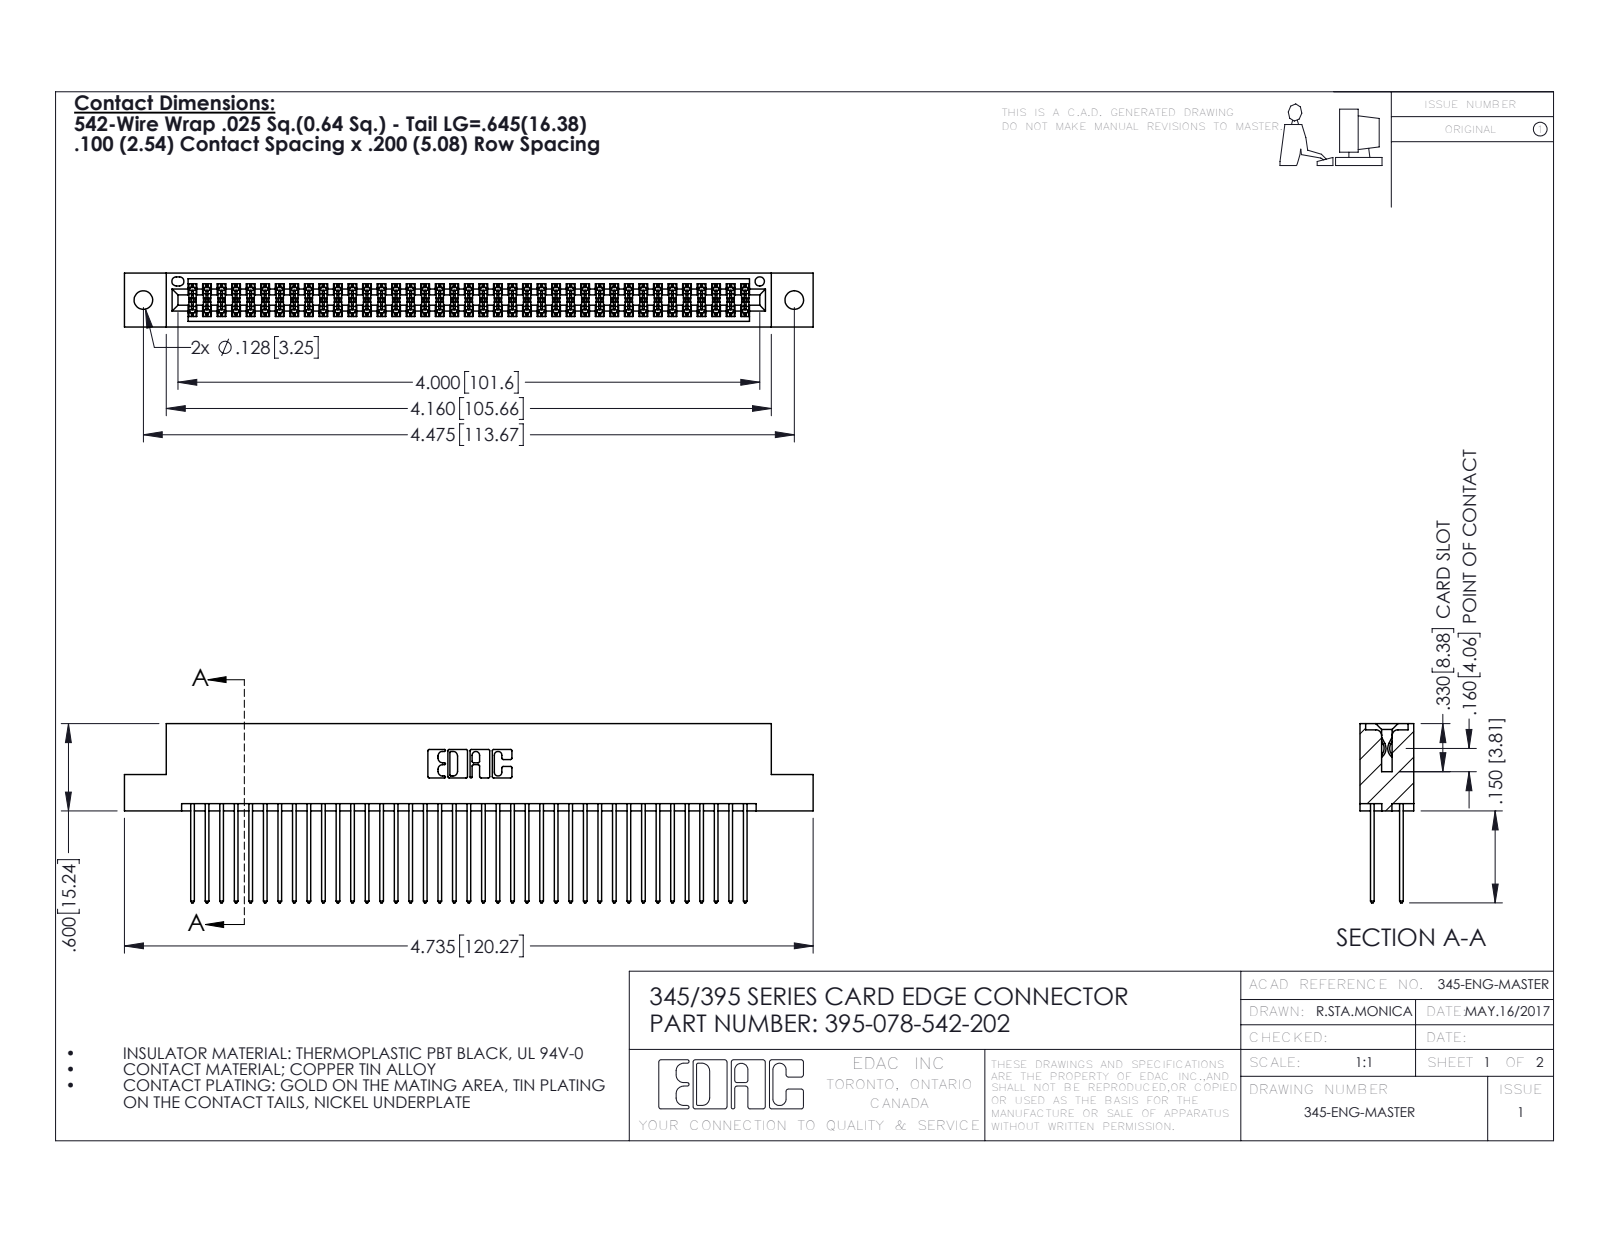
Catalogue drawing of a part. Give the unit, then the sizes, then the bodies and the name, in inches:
Units: inches
Overall size (bounding box): 4.735 × 1.232 × 0.37
Round holes (diameter × count): ⌀0.128 ×2, ⌀0.064 ×1
Partial cylindrical surfaces — rounded edges, fillets, slot ends (radius × count): R0.006 ×117, R0.01 ×78, R0.01 ×22, R0.007 ×6, R0.031 ×6, R0.026 ×3, R0.014 ×2, R0.019 ×2
Main face-to-face distances: 0.298, 0.072, 0.2, 0.098, 0.272, 0.025, 0.37, 0.225, 0.175, 0.149
Hole centre spacings: 0.27, 4.239, 4.475
Volume: 0.731 in³ · Surface area: 29.57 in²
Bodies: 79 solids, 4026 faces (2654 planar, 1372 cylindrical, 0 other)
Part name (STEP PRODUCT): 345 Part_Flush Mounting Lugs - 0.128 Dia; 345-292-001_345-293-142; 395-078-542-202
STEP written by: SolidWorks 2016 (CONFIG_CONTROL_DESIGN)
